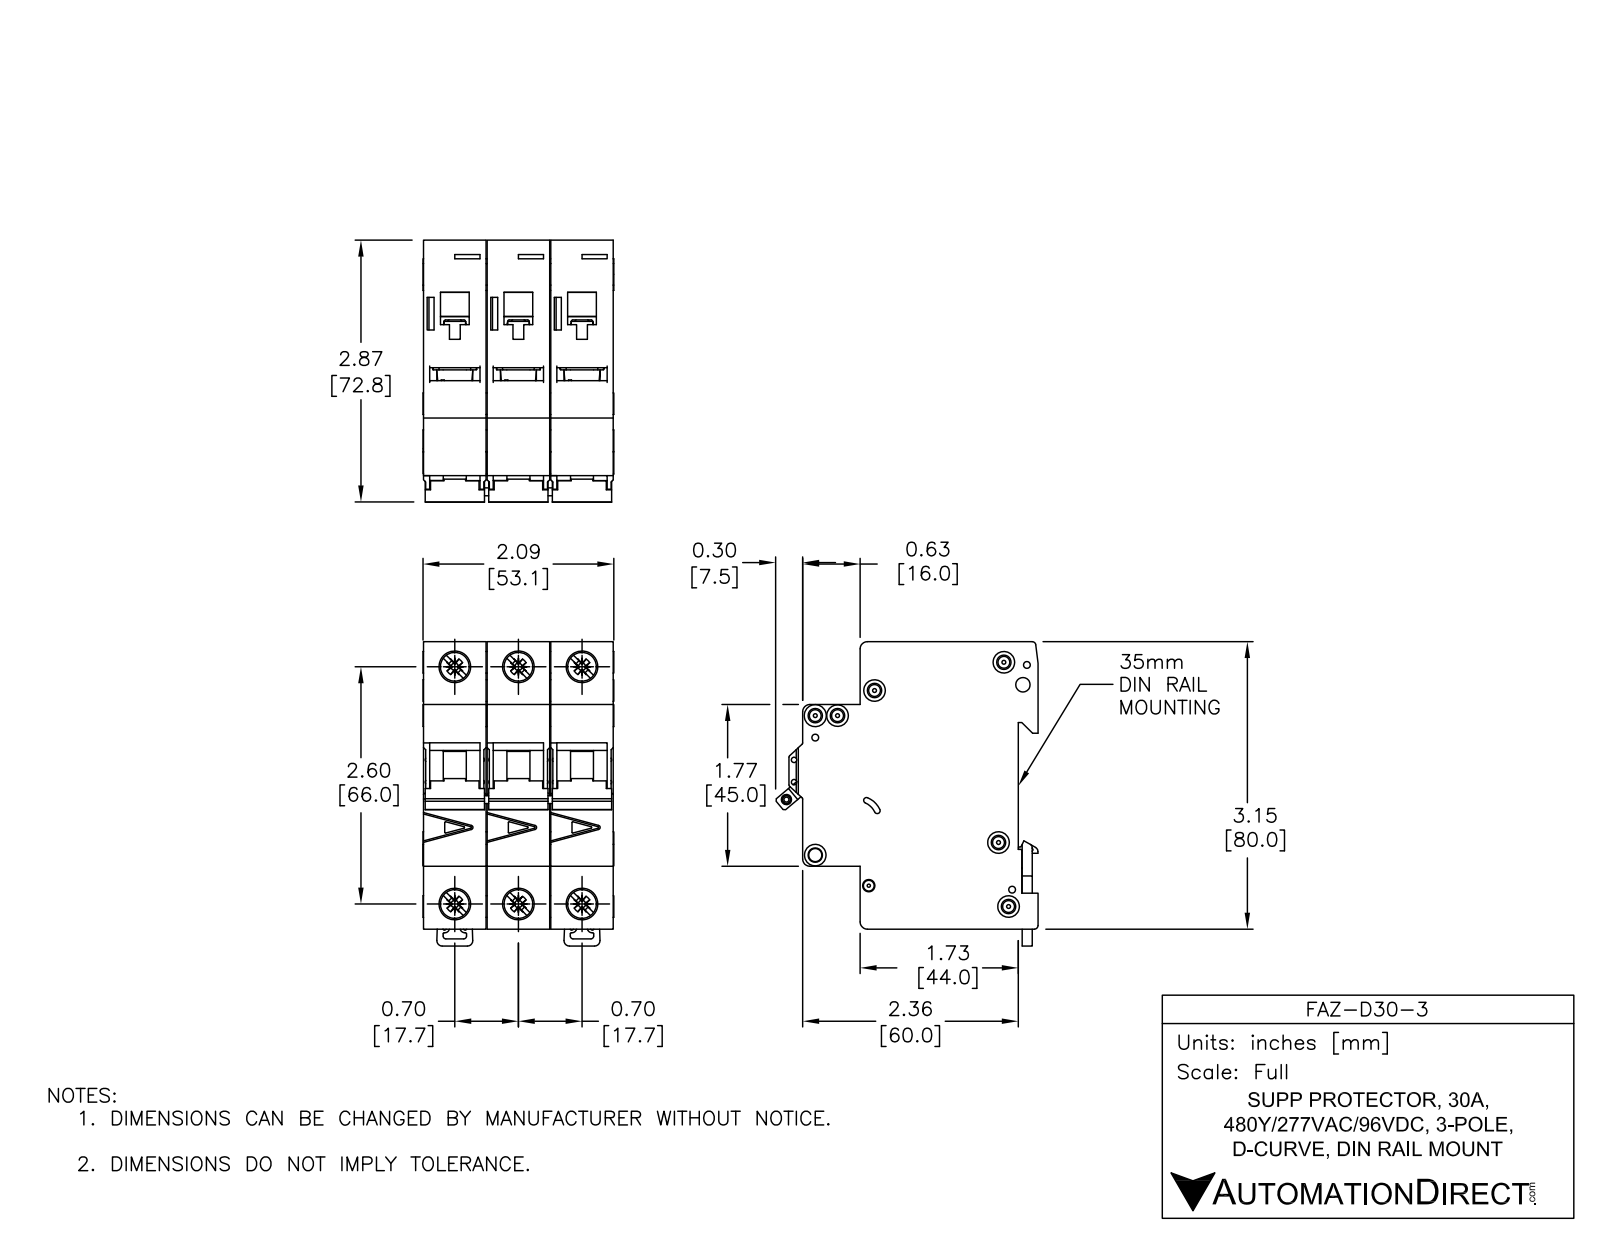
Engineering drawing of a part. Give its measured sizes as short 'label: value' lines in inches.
name: FAZ-D30-3
written by: SolidWorks 2014 (AUTOMOTIVE_DESIGN)
unit: in
bodies: 11 solids, 1650 faces (697 planar, 590 cylindrical, 363 other)
size: 3.338 × 2.876 × 2.091
volume: 13.71 in³; area: 89.98 in²
holes: 6× ⌀0.142, 4× ⌀0.323, 3× ⌀0.075, 2× ⌀0.043, 2× ⌀0.059, 2× ⌀0.157, 2× ⌀0.281, 1× ⌀0.085, 1× ⌀0.087, 1× ⌀0.1, 1× ⌀0.13, 1× ⌀0.134
bosses: 4× ⌀0.236, 3× ⌀0.098, 2× ⌀0.323
rounds: 68× R0.01, 25× R0.02, 12× R0.039, 12× R0.079, 11× R0.008, 3× R0.071, 2× R0.031, 2× R0.118
face distances: 0.697, 0.689, 1.394, 1.386, 2.083, 0.705, 3.129, 0.217, 1.949, 1.732
hole spacings: 0.697, 2.69, 2.598, 0.244, 0.537, 1.394, 2.948, 0.189
